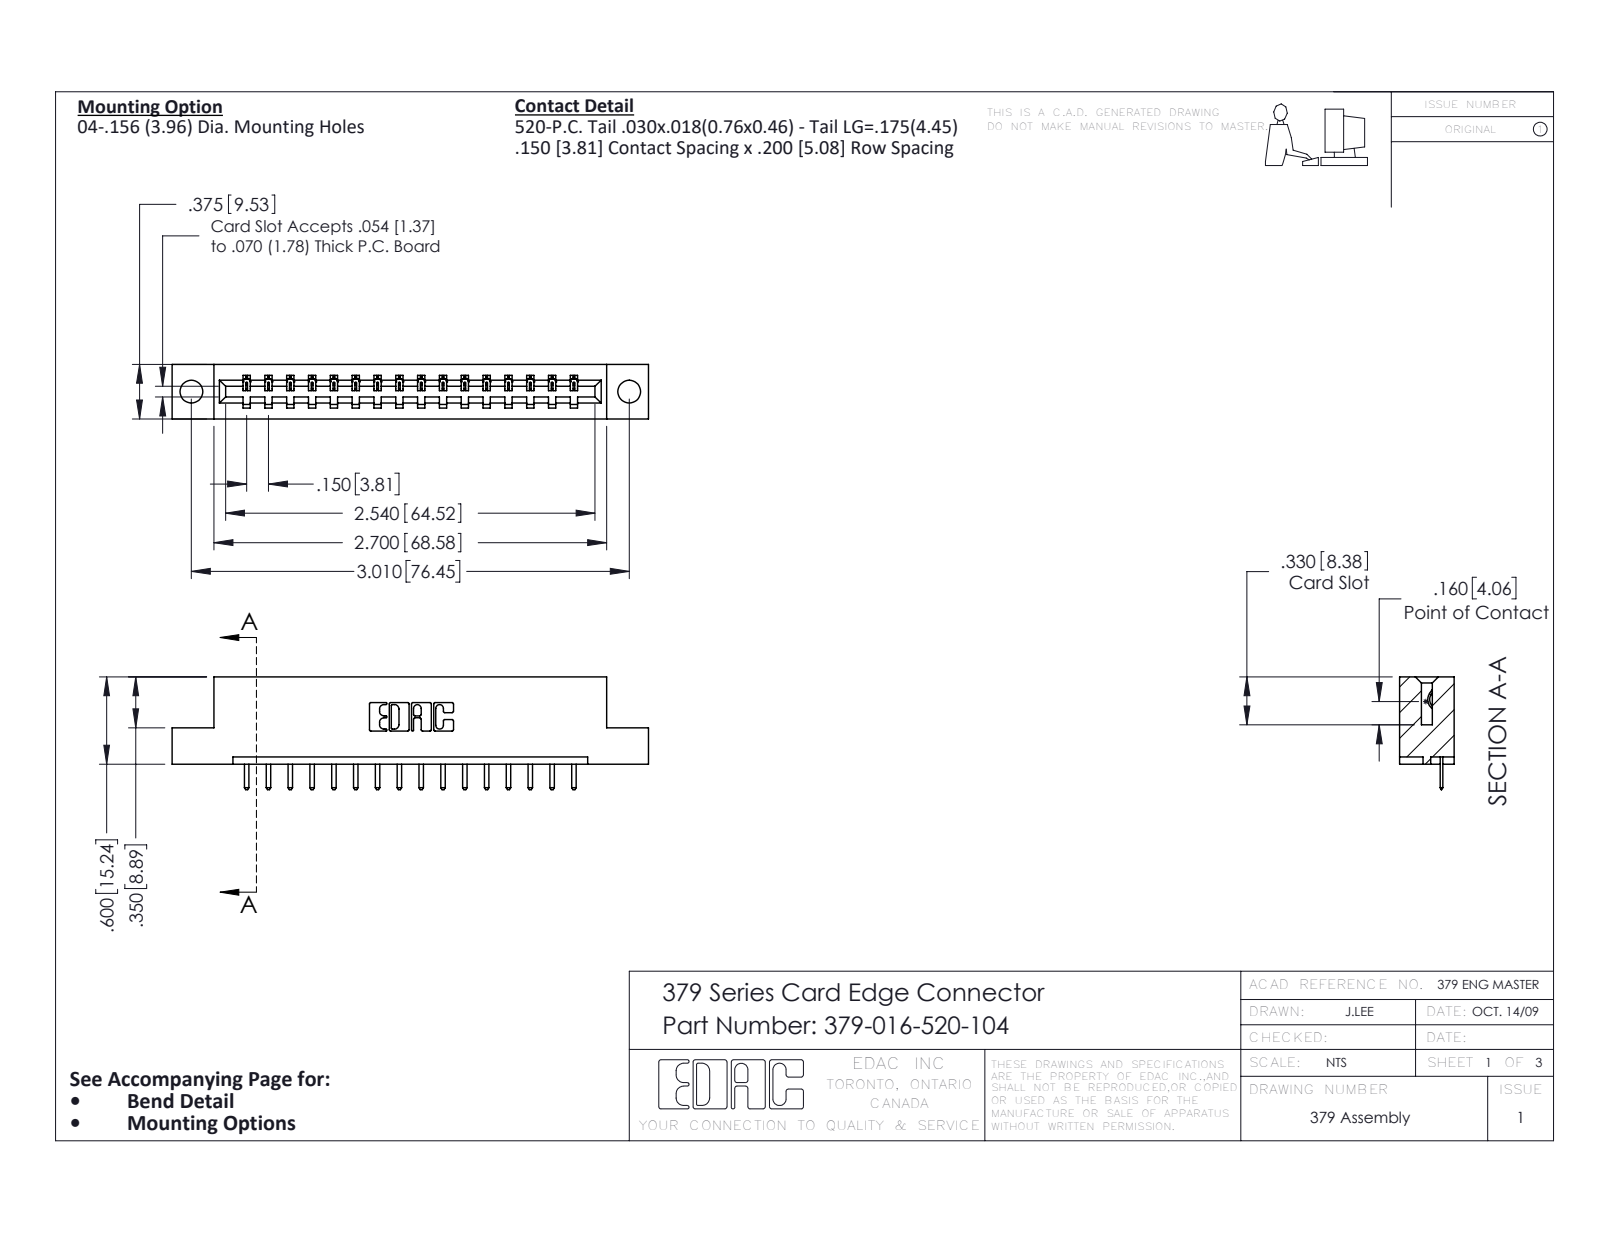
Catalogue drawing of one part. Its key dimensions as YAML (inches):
part_name: "379-016-520-104; 345-292-001_345-293-120; 379 Part_Flush - .156 Dia - TH"
step_written_by: "SolidWorks 2020 (CONFIG_CONTROL_DESIGN)"
units: inches
bodies: {solids: 17, faces: 1106, planar: 774, cylindrical: 332, other: 0}
overall_size: [3.275, 0.775, 0.375]
volume: 0.506
surface_area: 12.38
round_holes:
  - {diameter: 0.156, count: 2}
partial_cylinders:
  - {radius: 0.01, count: 34}
  - {radius: 0.006, count: 32}
  - {radius: 0.01, count: 22}
  - {radius: 0.007, count: 6}
  - {radius: 0.031, count: 6}
  - {radius: 0.026, count: 3}
  - {radius: 0.014, count: 1}
  - {radius: 0.022, count: 1}
face_to_face_distances: [0.3, 0.375, 0.075, 0.6, 0.15, 0.225, 0.45, 0.75, 0.2, 0.9]
hole_center_spacings: [3.01]
